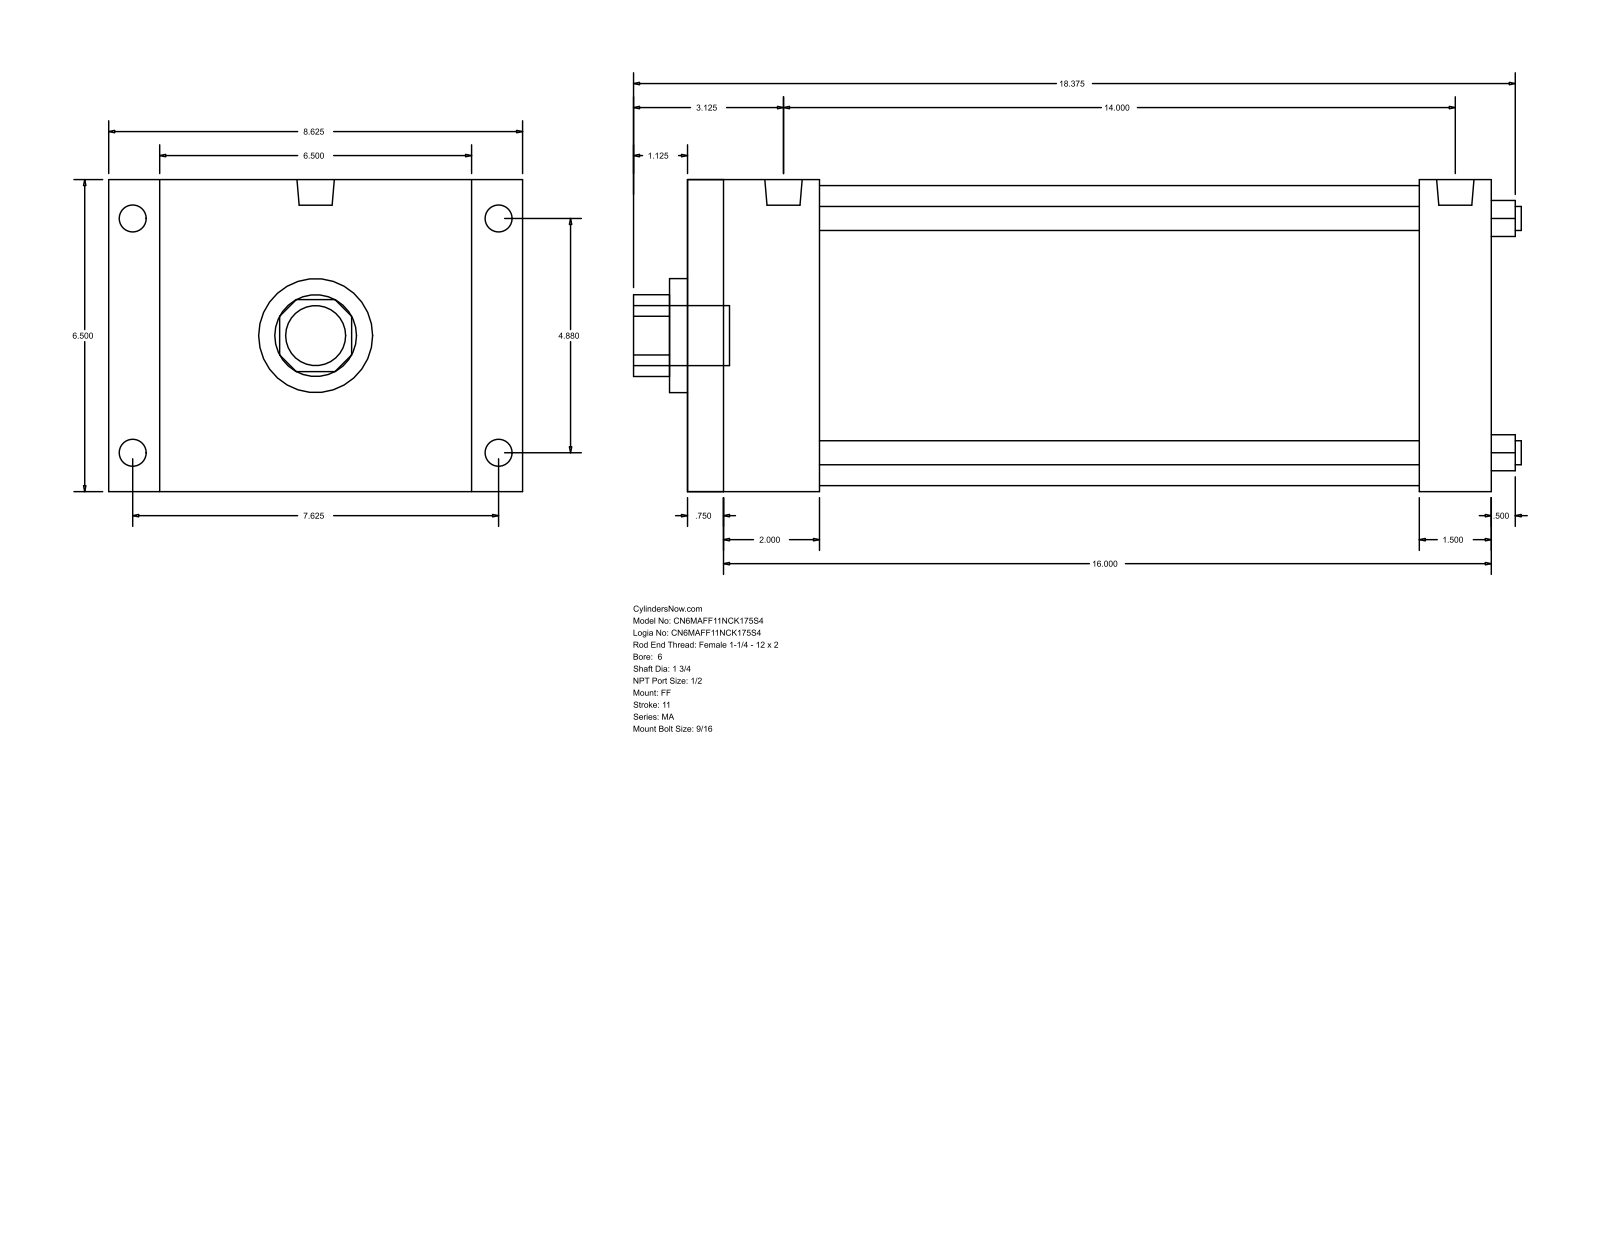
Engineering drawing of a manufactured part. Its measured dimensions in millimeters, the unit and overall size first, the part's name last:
Units: millimetres
Overall size (bounding box): 469.9 × 219.07 × 165.1
Round holes (diameter × count): ⌀12.7 ×4, ⌀44.45 ×1, ⌀60.33 ×1, ⌀158.75 ×1
Round bosses / shafts (diameter × count): ⌀17.46 ×4, ⌀14.29 ×4, ⌀19.77 ×2, ⌀31.75 ×1
Partial cylindrical surfaces — rounded edges, fillets, slot ends (radius × count): R21.63 ×1
Main face-to-face distances: 165.1, 425.45, 19.05, 406.4, 50.8, 368.31, 69.85, 355.6, 387.36, 317.51
Hole centre spacings: 87.65, 123.96, 175.31
Bodies: 0 solids, 92 faces (64 planar, 28 cylindrical, 0 other)
Part name (STEP PRODUCT): MA_FF__0600_1.75
STEP written by: GSSL Pune (CONFIG_CONTROL_DESIGN)
